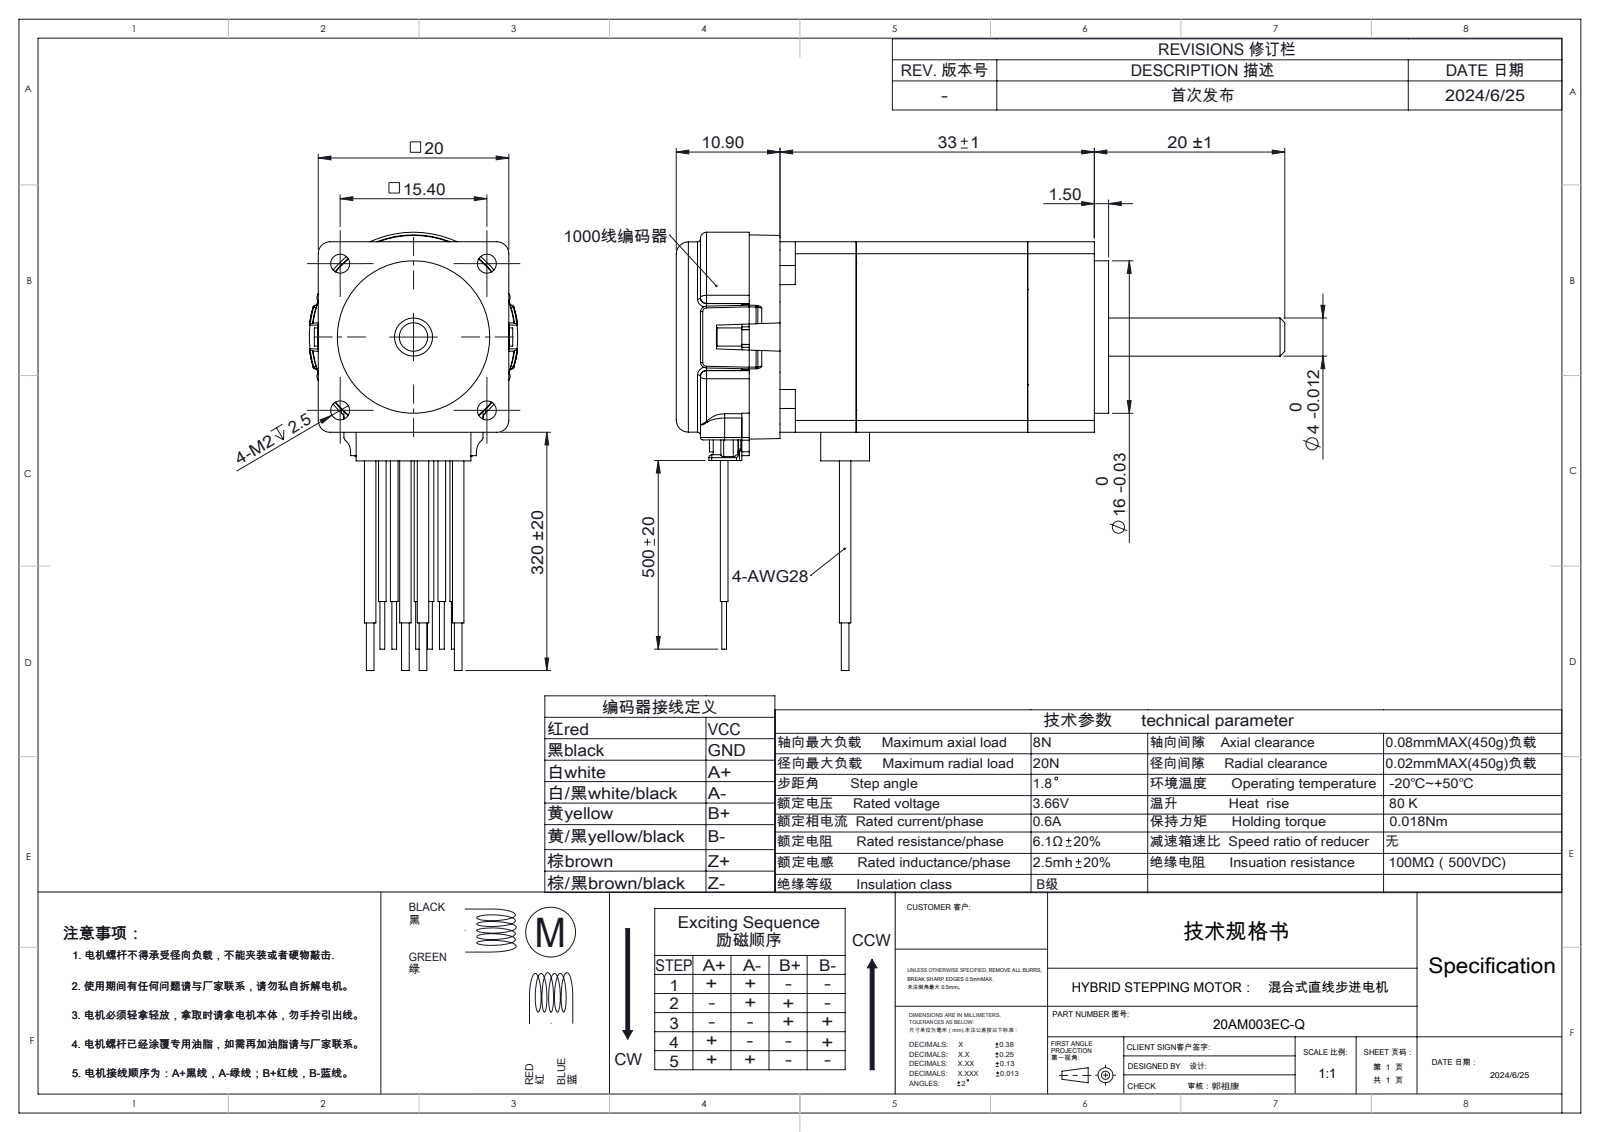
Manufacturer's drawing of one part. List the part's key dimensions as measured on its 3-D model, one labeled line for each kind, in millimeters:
Part name (STEP PRODUCT): 20AM003EC
STEP written by: SolidWorks 2024 (AUTOMOTIVE_DESIGN)
Units: millimetres
Bodies: 8 solids, 1182 faces (804 planar, 251 cylindrical, 127 other)
Overall size (bounding box): 63.9 × 46 × 21.88
Volume: 15 613 mm³ · Surface area: 10 470 mm²
Round holes (diameter × count): ⌀2 ×4, ⌀1.8 ×2, ⌀2.79 ×2, ⌀1.57 ×1, ⌀5 ×1, ⌀5.21 ×1, ⌀5.21 ×1, ⌀8.13 ×1, ⌀8.33 ×1, ⌀18.19 ×1
Round bosses / shafts (diameter × count): ⌀0.8 ×12, ⌀0.5 ×8, ⌀1.2 ×4, ⌀19.96 ×1, ⌀16 ×1, ⌀15.35 ×1, ⌀12.7 ×1, ⌀10.02 ×1
Partial cylindrical surfaces — rounded edges, fillets, slot ends (radius × count): R0.64 ×14, R0.3 ×7, R0.25 ×5, R0.3 ×4, R1.25 ×4, R1.91 ×4, R2 ×4, R0.13 ×2
Main face-to-face distances: 20, 26, 3.23, 29.23, 8, 18, 11.23, 0.79, 4.02, 12.02
Hole centre spacings: 10.57, 10.89, 15.4, 4.13, 4.17, 7.45, 7.5, 7.73
